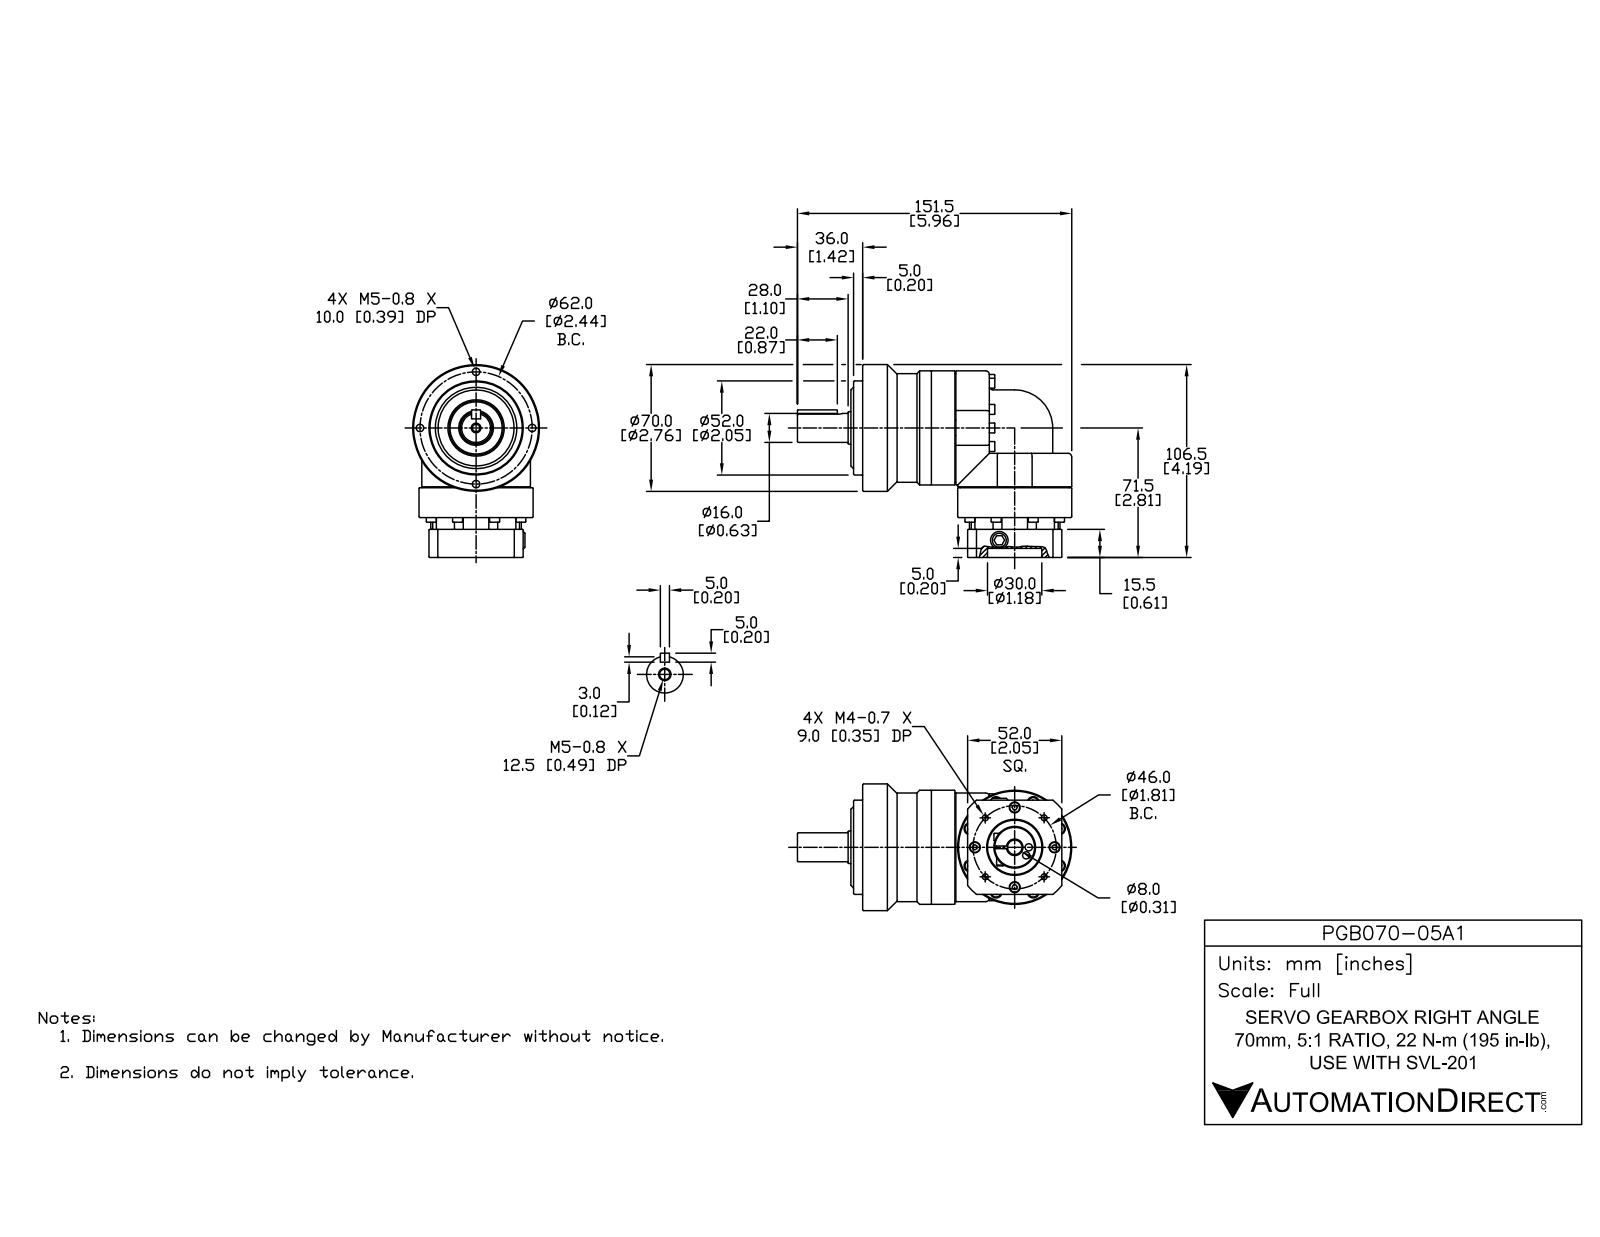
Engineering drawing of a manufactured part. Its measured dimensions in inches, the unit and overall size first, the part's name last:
Units: inches
Overall size (bounding box): 5.965 × 4.193 × 2.756
Round holes (diameter × count): ⌀0.138 ×8, ⌀0.256 ×8, ⌀0.163 ×5, ⌀0.128 ×4, ⌀0.236 ×4, ⌀0.157 ×2, ⌀0.315 ×2, ⌀0.177 ×1, ⌀1.181 ×1, ⌀1.339 ×1
Round bosses / shafts (diameter × count): ⌀0.217 ×21, ⌀0.118 ×8, ⌀2.48 ×2, ⌀2.362 ×2, ⌀2.756 ×1, ⌀2.047 ×1, ⌀0.906 ×1, ⌀0.709 ×1
Partial cylindrical surfaces — rounded edges, fillets, slot ends (radius × count): R0.079 ×6, R0.827 ×2, R0.098 ×1, R0.157 ×1, R0.984 ×1, R1.319 ×1
Main face-to-face distances: 0.256, 0.61, 2.205, 0.157, 0.197, 2.047, 2.264, 1.398, 1.654, 0.866
Hole centre spacings: 0.409, 0.417, 0.679, 1.053, 1.078, 1.095, 1.489, 1.599
Volume: 25.73 in³ · Surface area: 77.03 in²
Bodies: 1 solid, 700 faces (281 planar, 191 cylindrical, 228 other)
Part name (STEP PRODUCT): PGB070-05A1
STEP written by: SolidWorks 2014 (AUTOMOTIVE_DESIGN)
